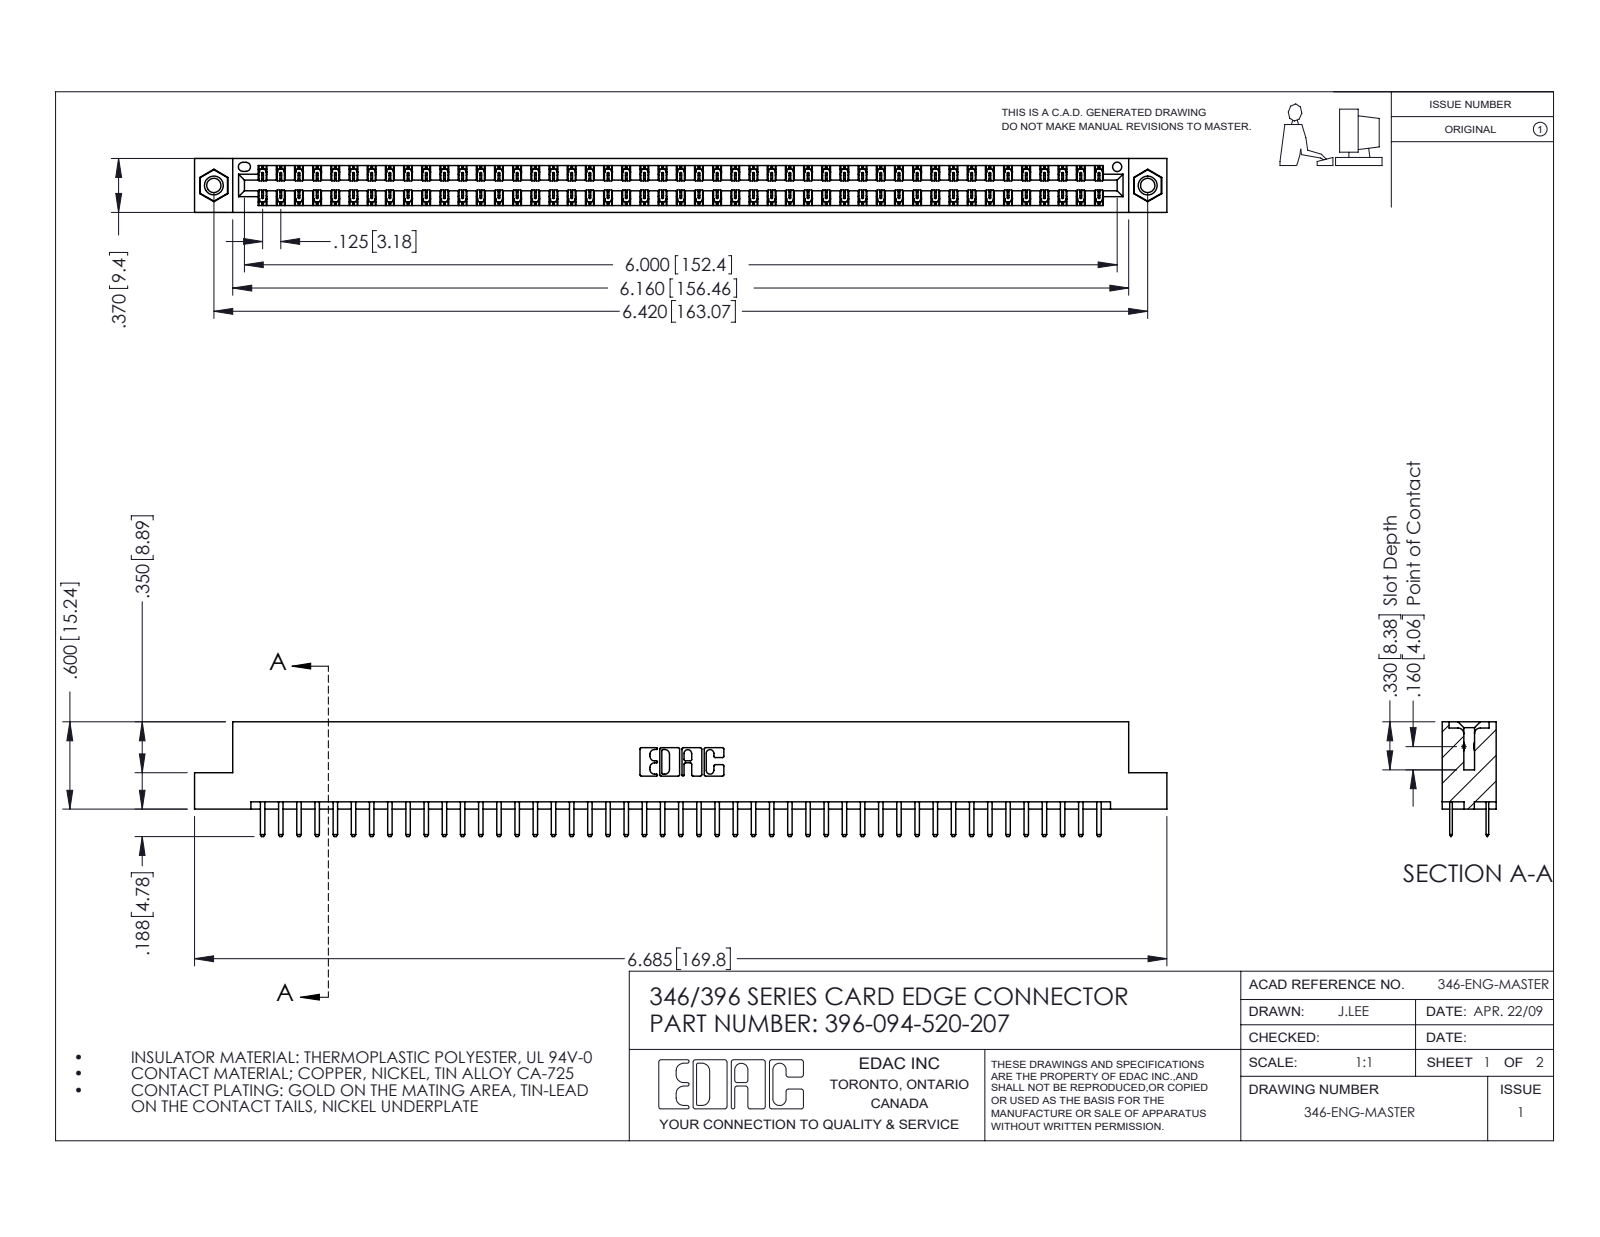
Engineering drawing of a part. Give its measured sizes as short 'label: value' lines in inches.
name: 346 Part_Flush Mounting Lugs - 0.156 Dia-TI; 396-094-520-207; 345-292-001_345-293-120; 345-250-001_345-250-005-103
written by: SolidWorks 2016 (CONFIG_CONTROL_DESIGN)
unit: in
bodies: 97 solids, 5446 faces (3586 planar, 1844 cylindrical, 16 other)
size: 6.685 × 0.788 × 0.37
volume: 1.009 in³; area: 35.27 in²
holes: 2× ⌀0.098, 2× ⌀0.125, 2× ⌀0.156, 1× ⌀0.064
bosses: 2× ⌀0.155
rounds: 141× R0.006, 98× R0.01, 22× R0.01, 6× R0.007, 6× R0.031, 3× R0.026, 2× R0.014, 2× R0.022
face distances: 0.048, 0.322, 0.25, 0.37, 0.275, 0.072, 0.298, 0.025, 0.148, 0.222
hole spacings: 0.246, 6.211, 6.42
